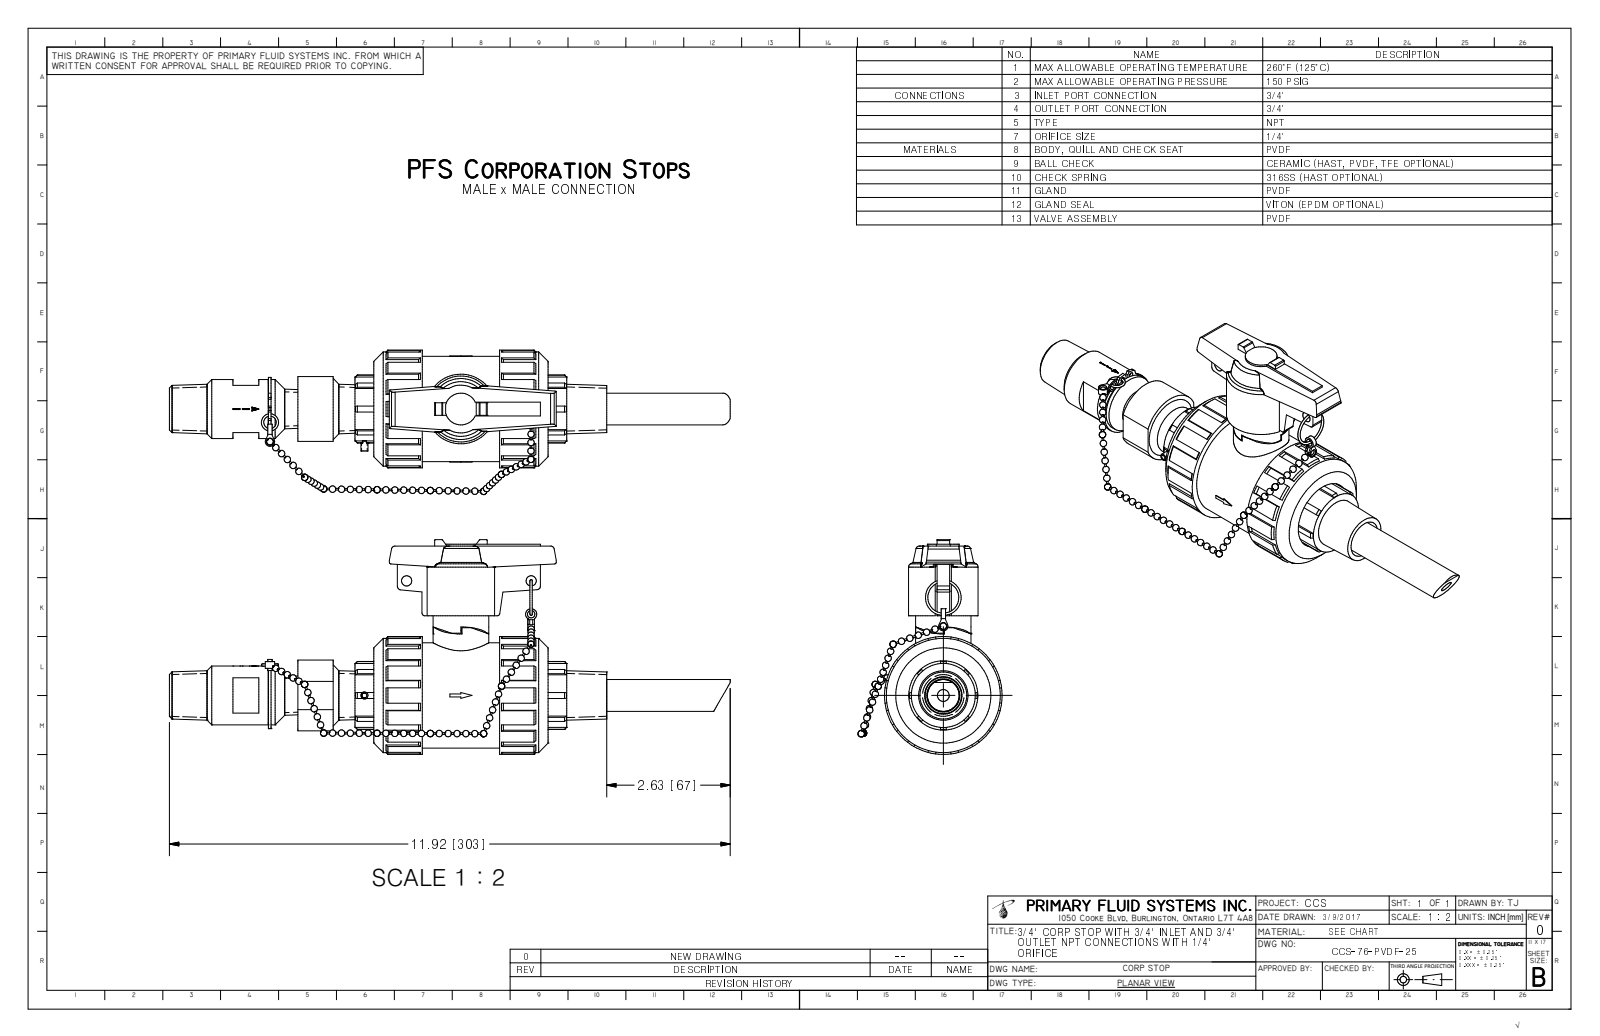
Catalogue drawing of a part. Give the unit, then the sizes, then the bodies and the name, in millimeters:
Units: millimetres
Overall size (bounding box): 302.8 × 115.7 × 77.8
Round holes (diameter × count): ⌀2.5 ×1, ⌀5.5 ×1, ⌀6.4 ×1, ⌀11.9 ×1, ⌀14.2 ×1, ⌀37.3 ×1, ⌀54.9 ×1
Round bosses / shafts (diameter × count): ⌀63.5 ×1, ⌀61.5 ×1, ⌀56.7 ×1, ⌀45.7 ×1, ⌀37.5 ×1, ⌀34.5 ×1, ⌀34.1 ×1, ⌀31.8 ×1
Partial cylindrical surfaces — rounded edges, fillets, slot ends (radius × count): R0.5 ×4, R2 ×4, R1 ×2, R1.4 ×2, R1.5 ×2, R5 ×2, R8.6 ×1, R15.8 ×1
Main face-to-face distances: 1, 6.8, 7.8, 12, 82.1, 5.8, 88.3, 6.1, 76.3, 26.2
Hole centre spacings: 16.7
Volume: 427 200 mm³ · Surface area: 77 550 mm²
Bodies: 1 solid, 599 faces (293 planar, 77 cylindrical, 229 other)
Part name (STEP PRODUCT): CCS-76-PVDF-25_R0
STEP written by: Autodesk Inventor 2009 (AUTOMOTIVE_DESIGN)
